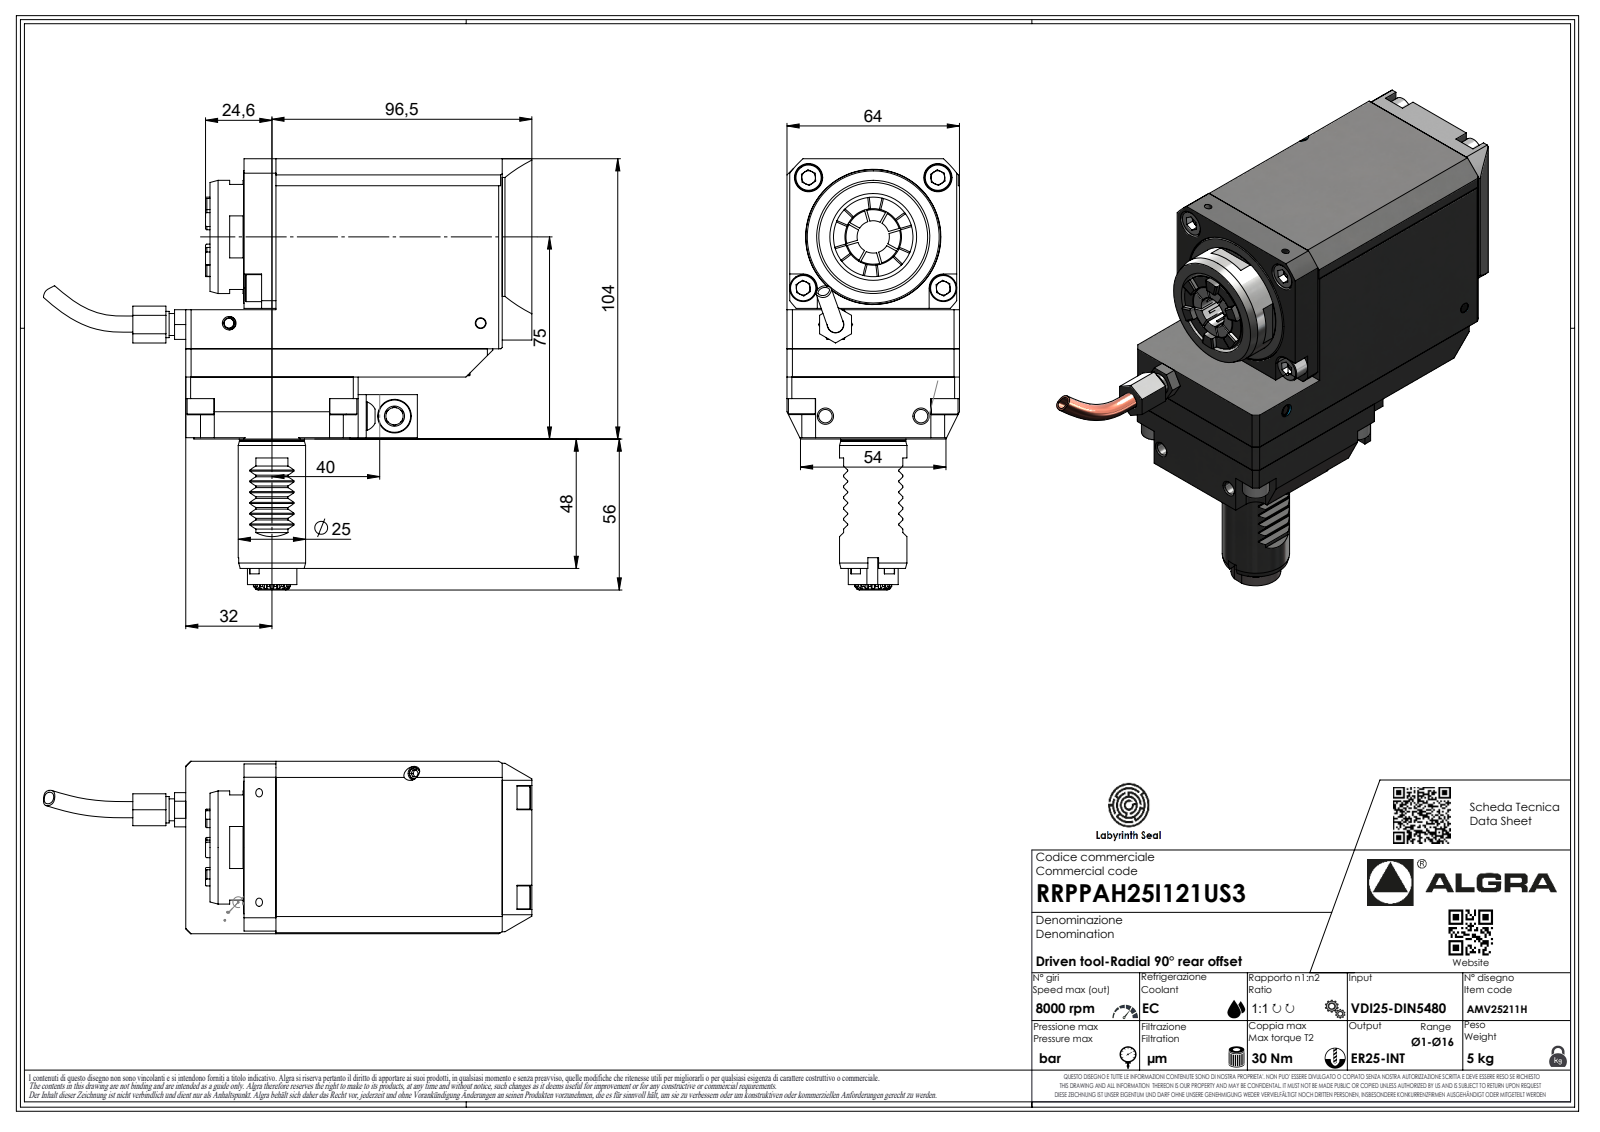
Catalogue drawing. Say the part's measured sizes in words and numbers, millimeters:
The part is named "RRPPAH25I121US3". Its 3-D file was written by "SolidWorks 2023 (AUTOMOTIVE_DESIGN)". It is 1 solid with 769 faces: 500 planar, 146 cylindrical and 123 other. Overall it measures 181.31 by 160 by 64 millimeters. Its volume is 697 124 cubic millimeters and its surface area 61 024 square millimeters. Round holes: 1 of diameter 2.1, 1 of diameter 22. Round bosses or shafts: 1 of diameter 42, 1 of diameter 25, 1 of diameter 24.1, 1 of diameter 18.5, 1 of diameter 11, 1 of diameter 9.8, 1 of diameter 8.15, 1 of diameter 6.37. Partial cylindrical surfaces (rounded edges, fillets, slot ends): 12 of radius 0.3, 10 of radius 35, 7 of radius 0.33, 7 of radius 0.52, 7 of radius 3.7, 4 of radius 5.1, 4 of radius 5.25, 2 of radius 4.5. The main face-to-face distances are 64, 48, 128.5, 25, 0.5, 81, 56, 104, 23, 107.
